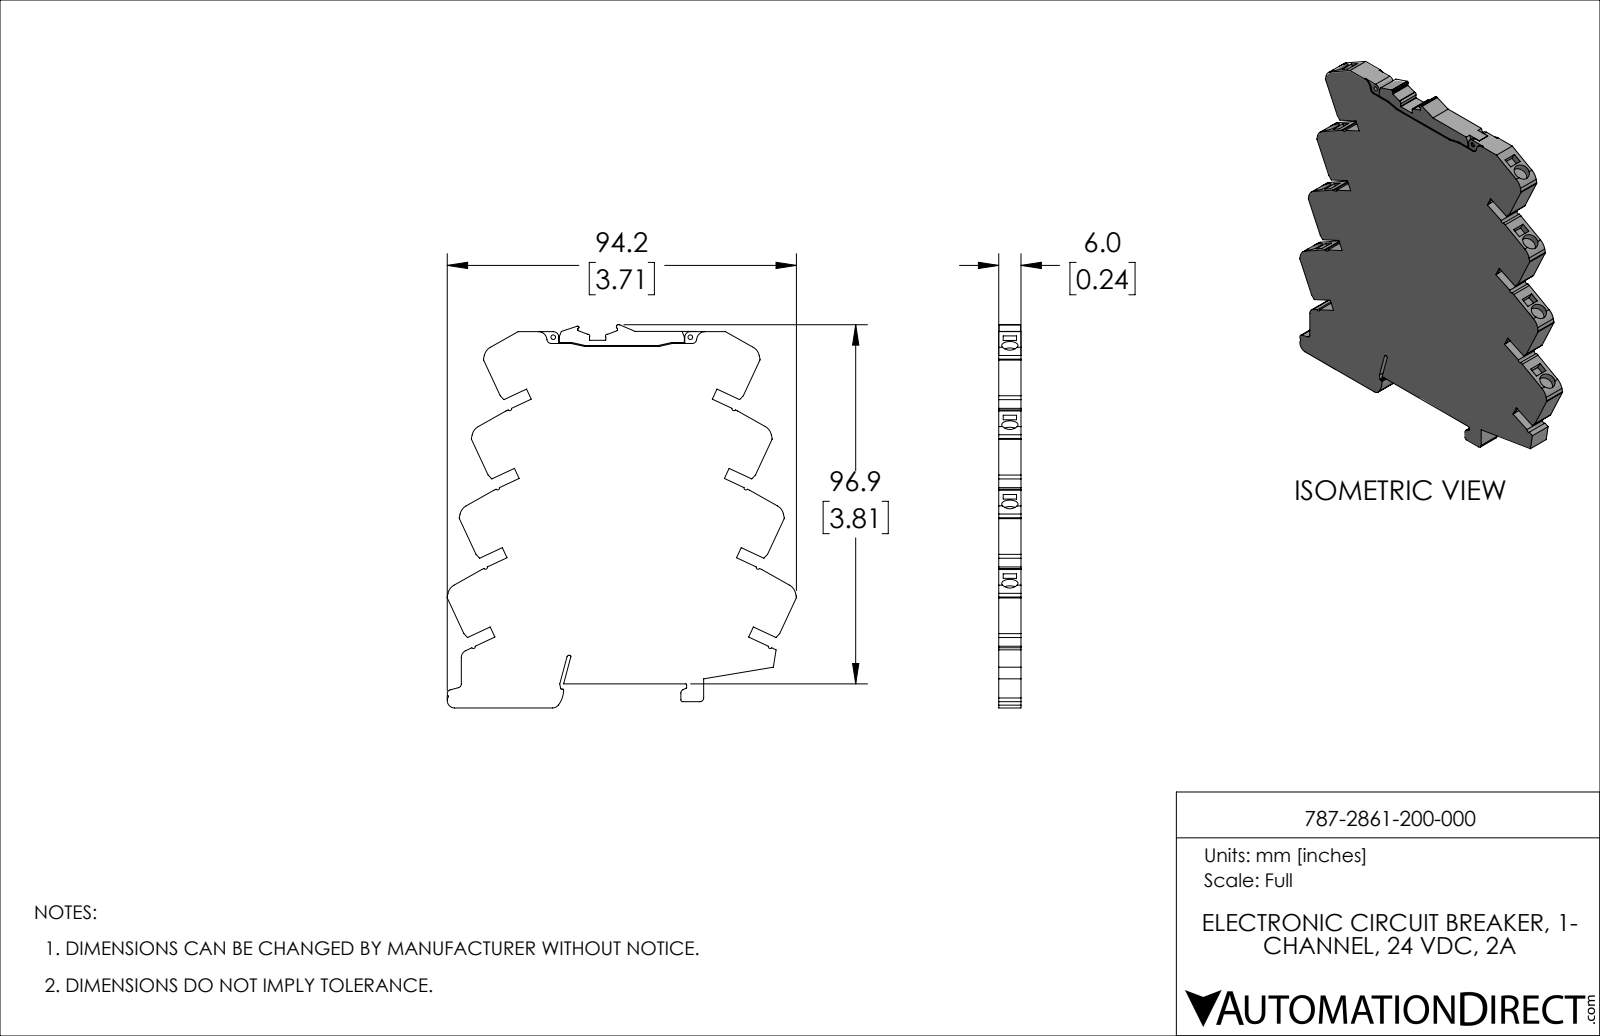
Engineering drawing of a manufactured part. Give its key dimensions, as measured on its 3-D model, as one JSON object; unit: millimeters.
{"part_name": "787-2861/200-000", "step_written_by": "PARTsolutions (CONFIG_CONTROL_DESIGN)", "units": "millimeters", "bodies": {"solids": 1, "faces": 294, "planar": 219, "cylindrical": 75, "other": 0}, "overall_size": [103.36, 94.26, 6], "volume_mm3": 43932, "surface_area_mm2": 19262, "round_holes": [[4.4, 8], [1.25, 2]], "partial_cylinders_radius": [[0.5, 12], [0.2, 11], [0.4, 8], [3.35, 8], [1, 4], [0.3, 3], [2, 3], [0.45, 2]], "face_to_face_distances": [6, 17.99, 17.02, 12.01, 5.9, 12, 3, 24.01, 35.98, 6.5], "hole_center_spacings": [13.35, 13.34, 26.7, 26.69, 26.71, 37, 40.04, 40.05]}
